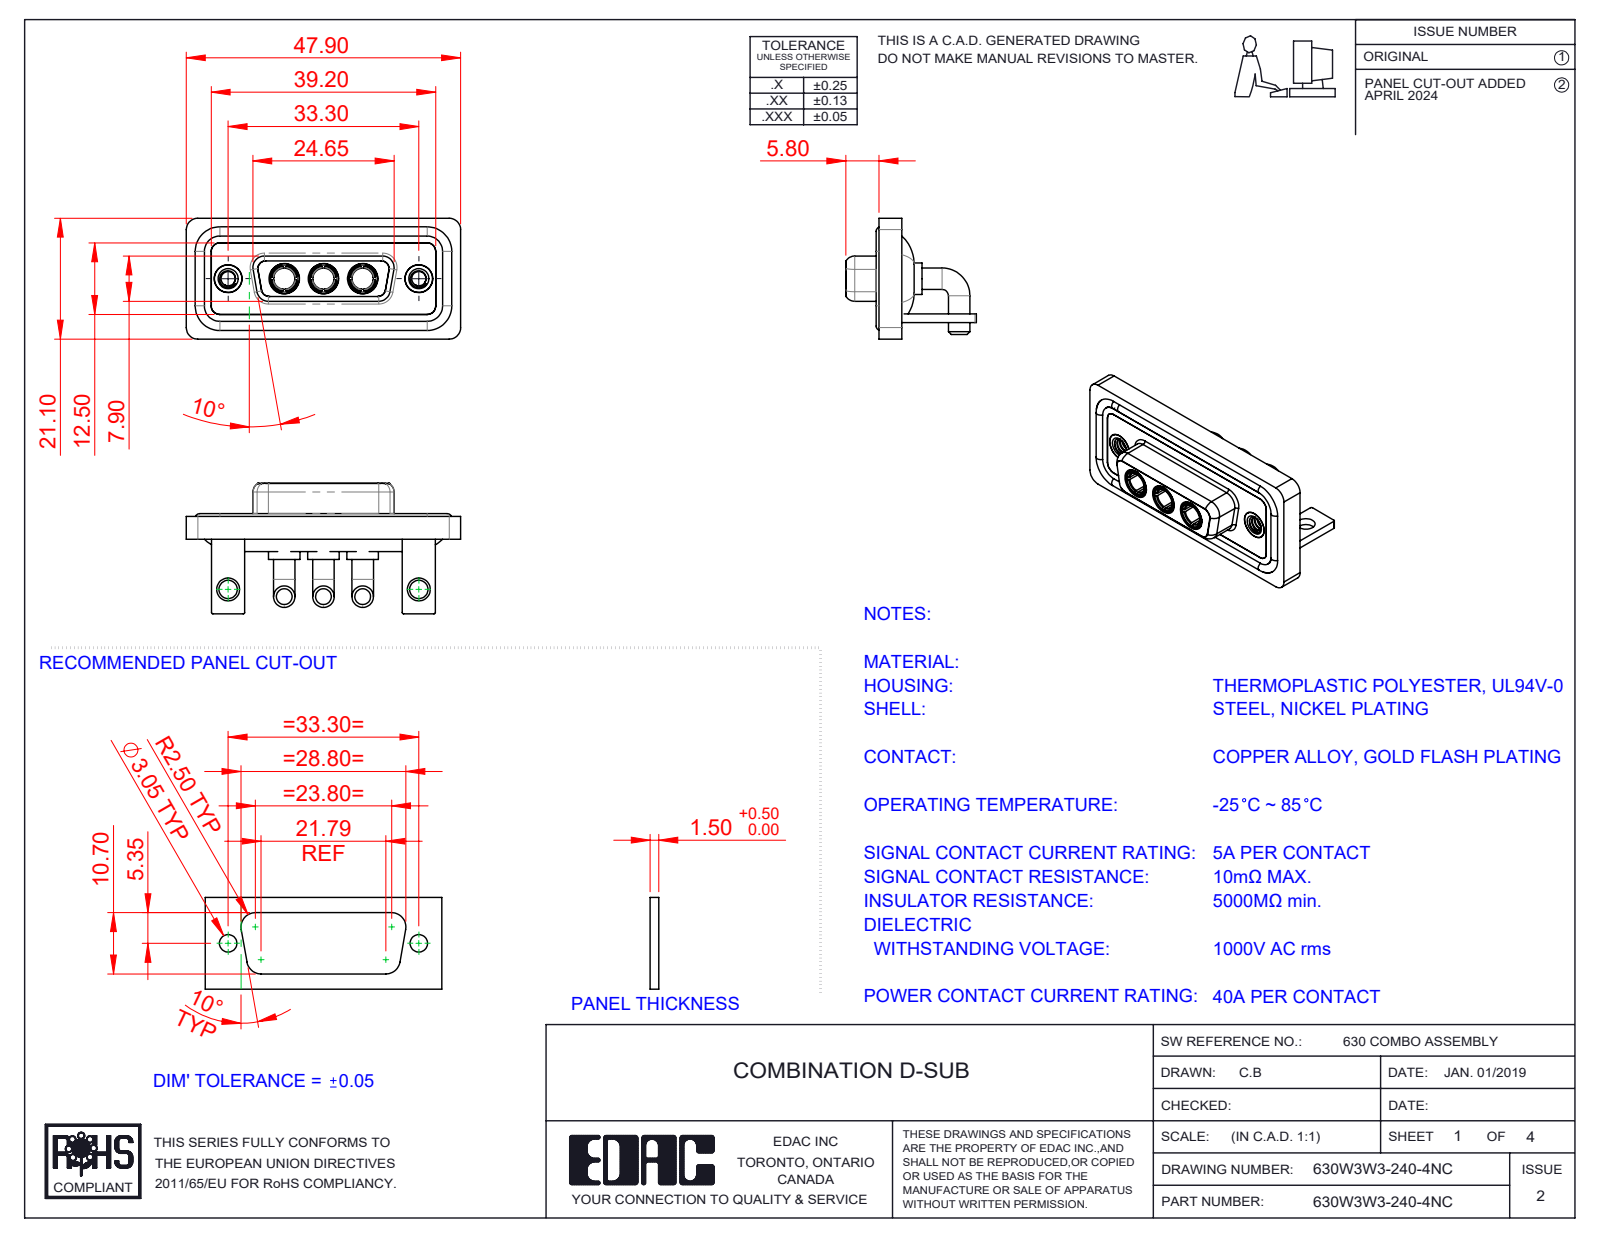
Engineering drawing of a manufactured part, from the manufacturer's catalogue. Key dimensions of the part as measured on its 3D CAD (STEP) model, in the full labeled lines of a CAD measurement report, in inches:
Part name (STEP PRODUCT): 630Combo Shell Front_15 Contacts; 630Combo Shell Rear_15 Contacts; 630W3W3-140-4NC; 630Combo Threaded Rivet_A (+4 more)
STEP written by: SolidWorks 2023 (CONFIG_CONTROL_DESIGN)
Units: inches
Bodies: 15 solids, 662 faces (212 planar, 285 cylindrical, 165 other)
Overall size (bounding box): 1.886 × 0.898 × 0.831
Volume: 0.412 in³ · Surface area: 16.81 in²
Round holes (diameter × count): ⌀0.191 ×5, ⌀0.146 ×3, ⌀0.209 ×3, ⌀0.098 ×2, ⌀0.126 ×2, ⌀0.157 ×2, ⌀0.159 ×2, ⌀0.197 ×2
Round bosses / shafts (diameter × count): ⌀0.148 ×6, ⌀0.063 ×4, ⌀0.217 ×3, ⌀0.205 ×3, ⌀0.195 ×3, ⌀0.187 ×3, ⌀0.195 ×2, ⌀0.189 ×2
Partial cylindrical surfaces — rounded edges, fillets, slot ends (radius × count): R0.079 ×21, R0.059 ×18, R0.01 ×16, R0.053 ×12, R0.063 ×8, R0.02 ×5, R0.024 ×4, R0.026 ×4
Main face-to-face distances: 0.016, 0.114, 0.059, 0.071, 0.146, 0.043, 0.161, 0.063, 0.098, 0.055
Hole centre spacings: 0.27, 0.386, 0.656, 0.925, 1.311, 0.539
